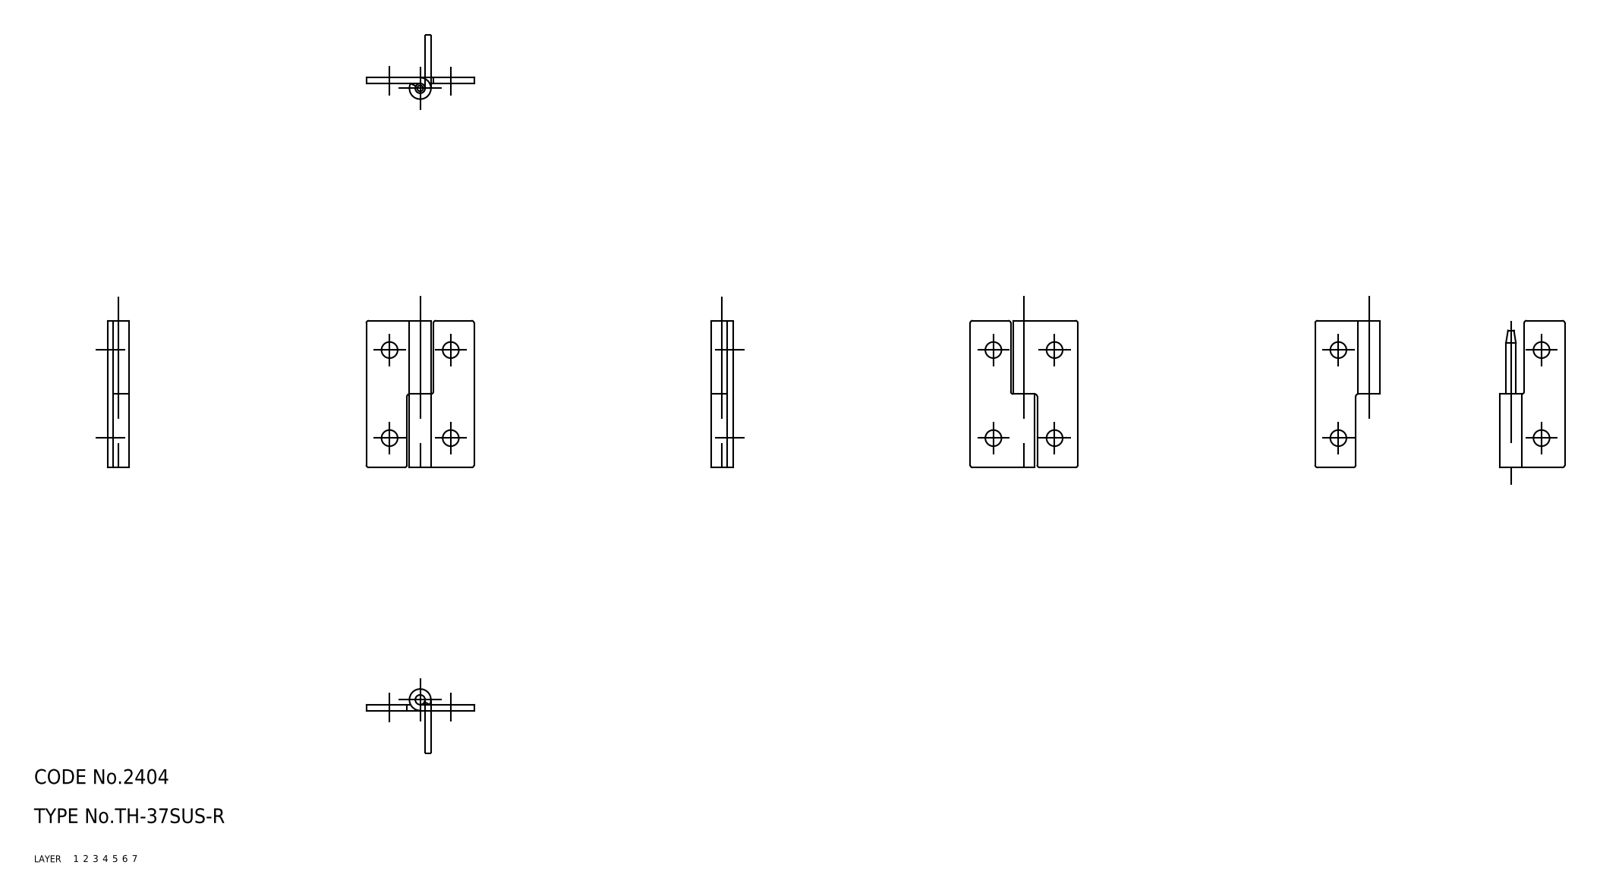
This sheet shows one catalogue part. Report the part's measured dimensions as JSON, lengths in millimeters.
{"part_name": "shaft; hinge piece_B; hinge piece_A; TH_37SUS_R_8500_36", "step_written_by": "CADfix (AUTOMOTIVE_DESIGN)", "units": "millimeters", "bodies": {"solids": 3, "faces": 42, "planar": 0, "cylindrical": 0, "other": 42}, "overall_size": [30, 22, 4.4], "volume_mm3": 1036, "surface_area_mm2": 2046}
